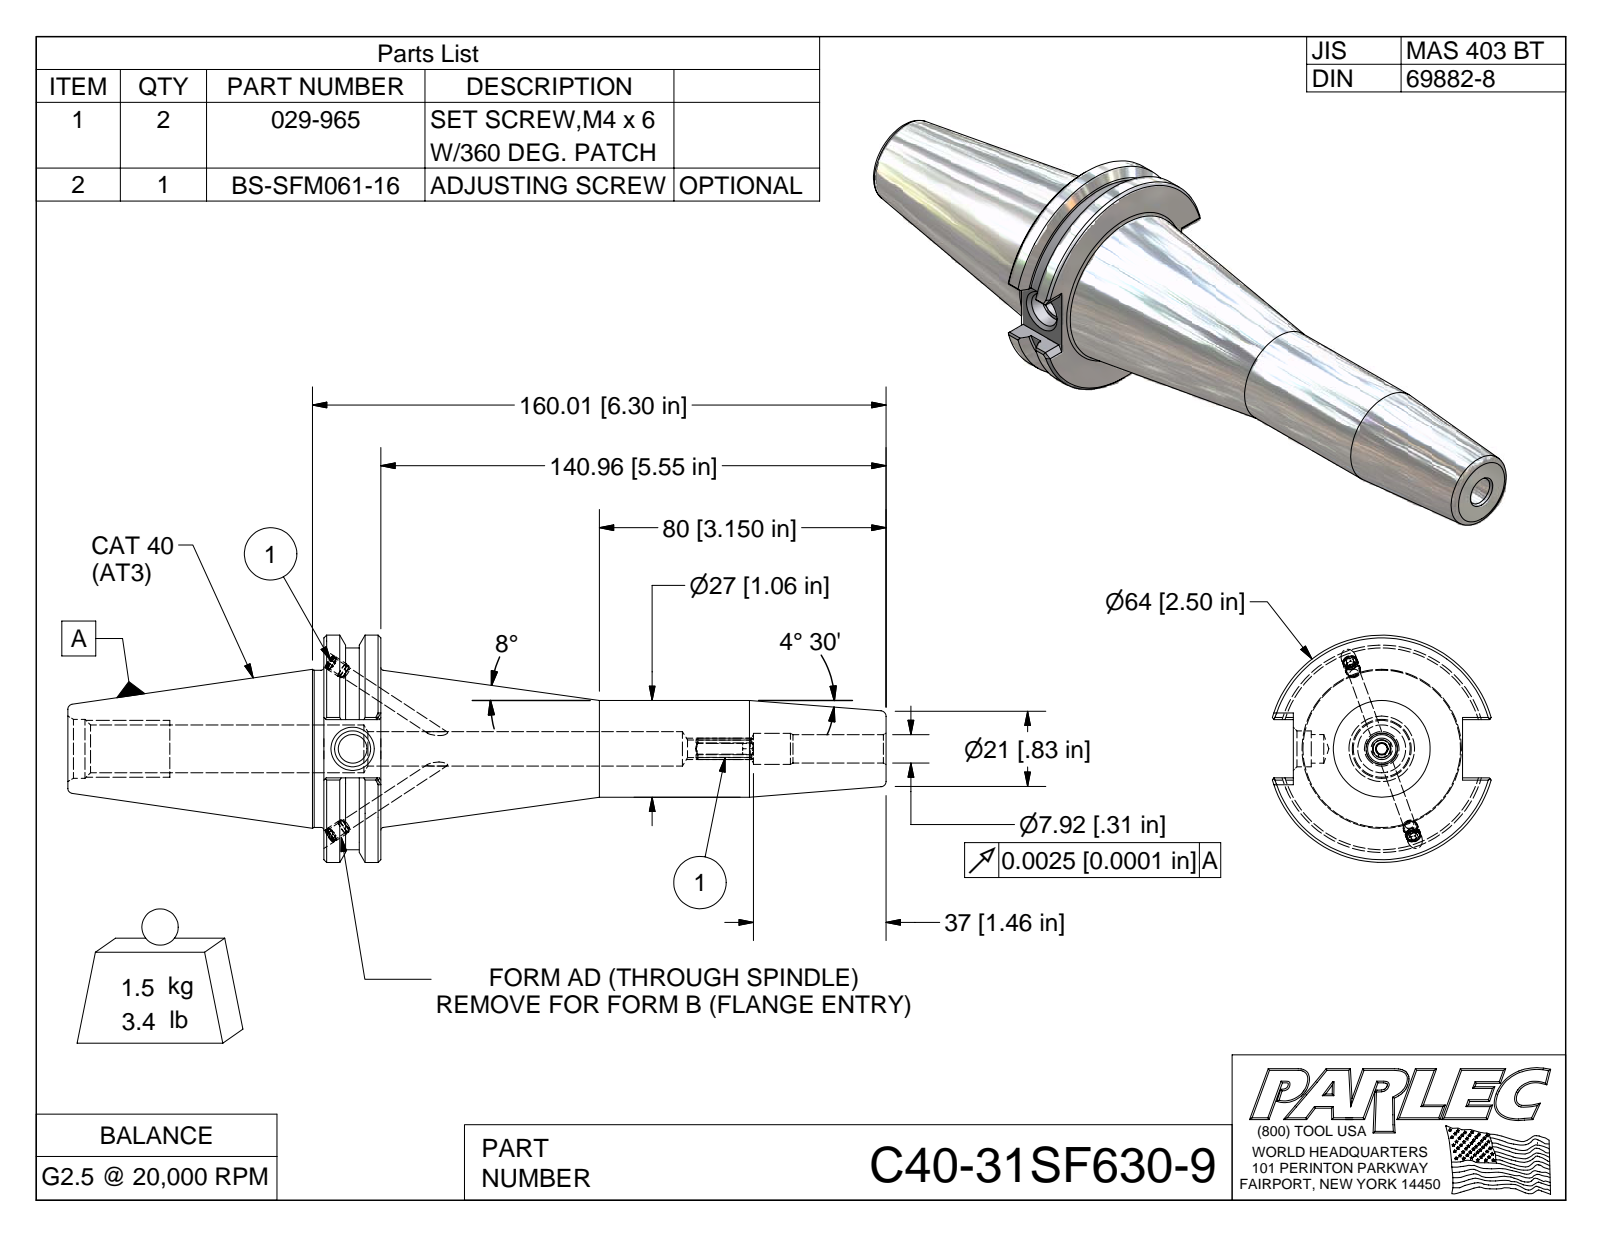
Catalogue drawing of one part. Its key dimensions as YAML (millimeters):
part_name: "C40-31SF630-9; C40BC-31SF630-9-1; 029-965; BS-SFM061-16"
step_written_by: "Autodesk Inventor 2009 (AUTOMOTIVE_DESIGN)"
units: millimeters
bodies: {solids: 4, faces: 138, planar: 65, cylindrical: 22, other: 51}
overall_size: [228.3, 63.5, 61]
volume: 194800
surface_area: 37660
round_holes:
  - {diameter: 3.3, count: 2}
  - {diameter: 4.1, count: 2}
  - {diameter: 7.9, count: 1}
  - {diameter: 8.7, count: 1}
round_bosses_or_shafts:
  - {diameter: 4.2, count: 2}
  - {diameter: 4, count: 2}
  - {diameter: 63.5, count: 1}
  - {diameter: 56.4, count: 1}
  - {diameter: 43.9, count: 1}
  - {diameter: 27, count: 1}
partial_cylinders:
  - {radius: 3, count: 1}
face_to_face_distances: [15.9, 156.8, 141, 16.3, 47.2, 71.4, 87.3, 228.3, 81.3, 9.9]
